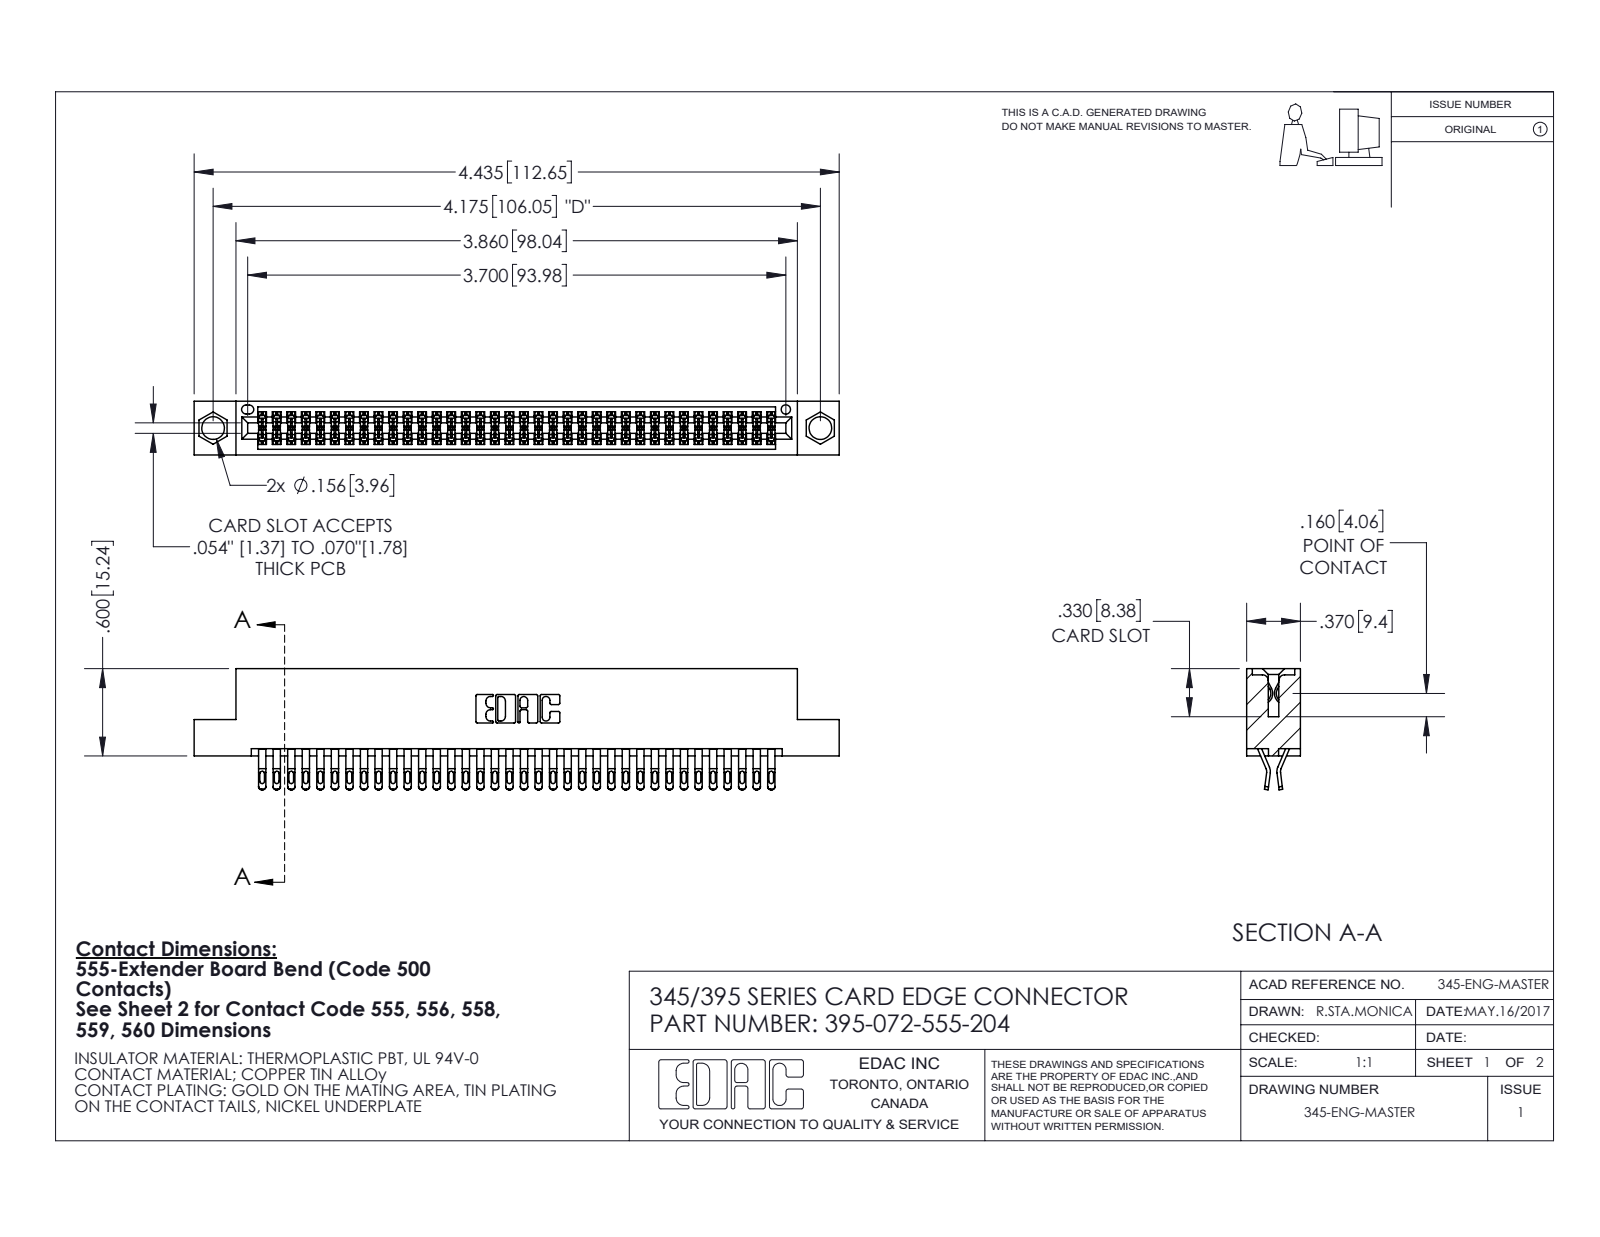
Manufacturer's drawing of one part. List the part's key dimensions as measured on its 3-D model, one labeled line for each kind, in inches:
Part name (STEP PRODUCT): 345-292-001_555 Tail; 345 Part_Flush Mounting Lugs - 0.156 Dia-TI; 395-072-555-204
STEP written by: SolidWorks 2020 (CONFIG_CONTROL_DESIGN)
Units: inches
Bodies: 73 solids, 4172 faces (2326 planar, 1846 cylindrical, 0 other)
Overall size (bounding box): 4.435 × 0.832 × 0.37
Volume: 0.671 in³ · Surface area: 25.9 in²
Round holes (diameter × count): ⌀0.156 ×2, ⌀0.064 ×1
Partial cylindrical surfaces — rounded edges, fillets, slot ends (radius × count): R0.016 ×180, R0.02 ×144, R0.006 ×108, R0.01 ×22, R0.007 ×6, R0.031 ×6, R0.026 ×3, R0.01 ×2
Main face-to-face distances: 0.298, 0.072, 0.37, 0.025, 0.2, 0.098, 0.272, 0.225, 0.175, 0.149
Hole centre spacings: 0.27, 3.939, 4.175
